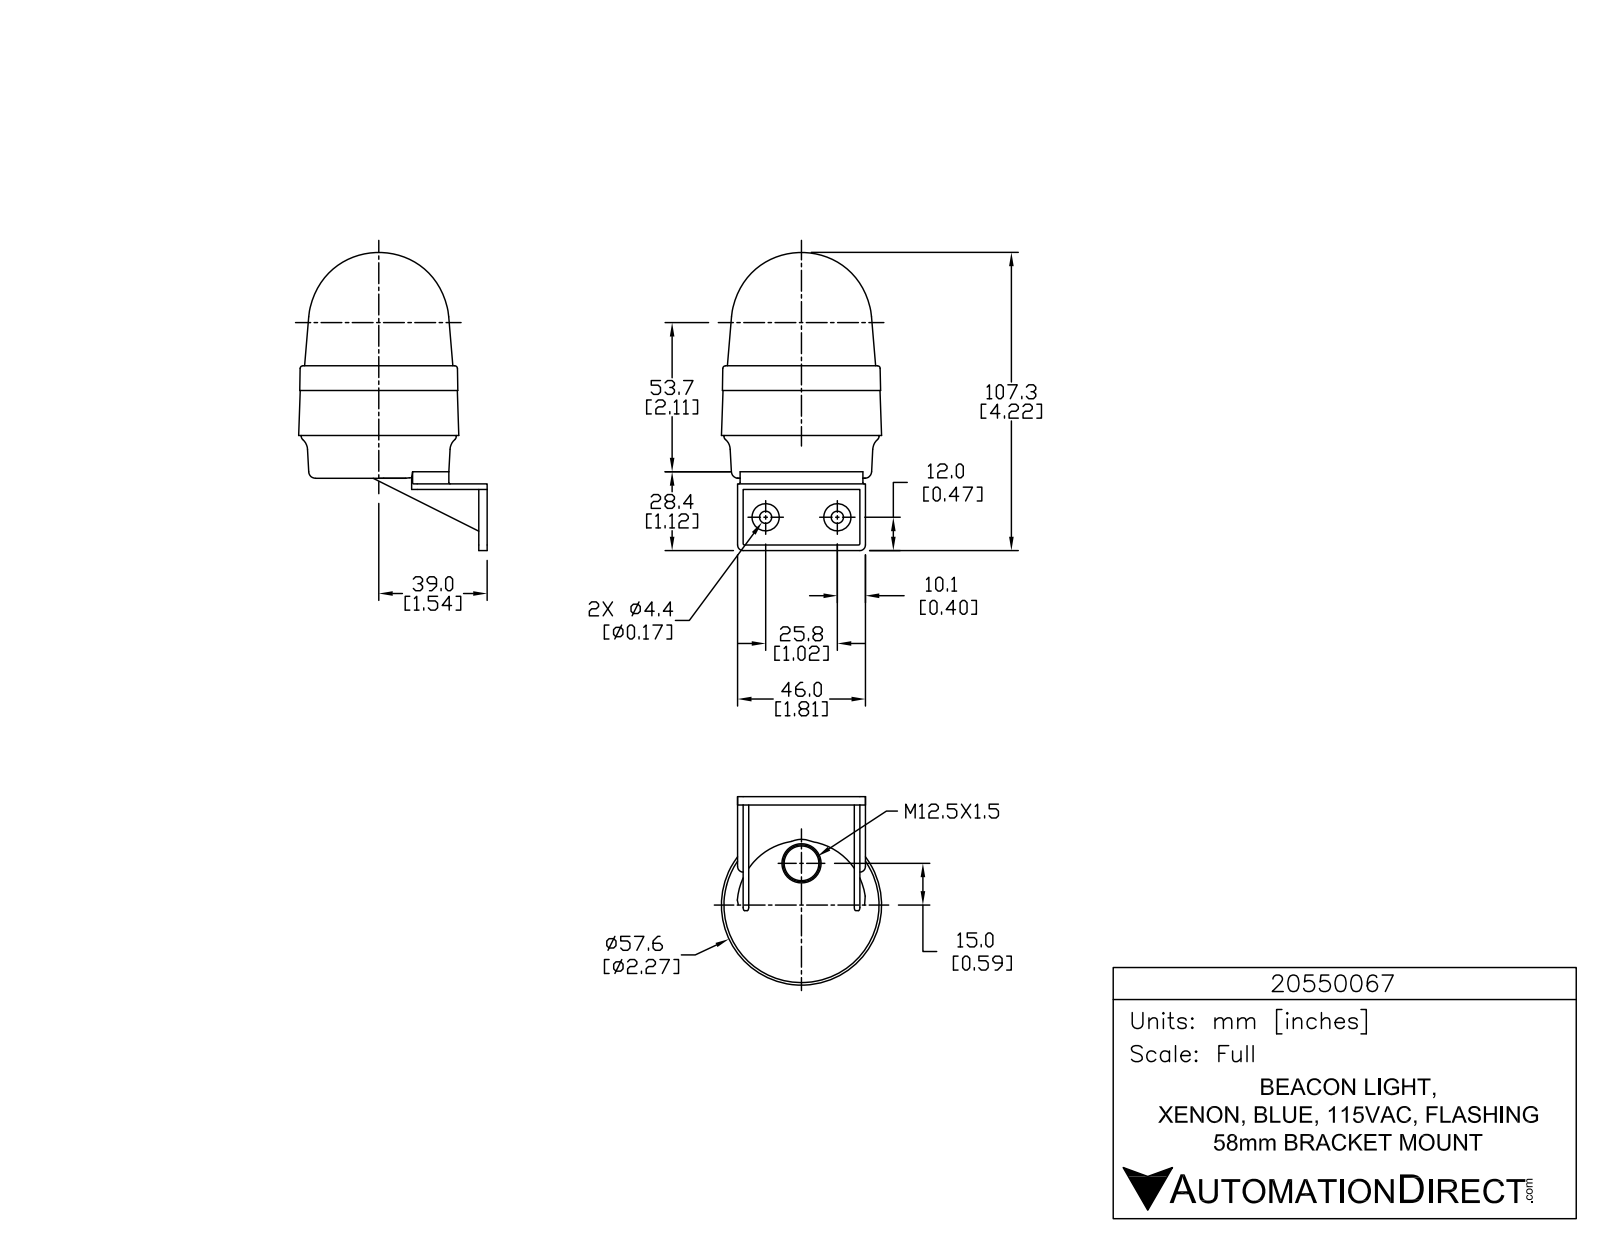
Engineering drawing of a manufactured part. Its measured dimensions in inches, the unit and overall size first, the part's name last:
Units: inches
Overall size (bounding box): 4.225 × 2.852 × 2.407
Round holes (diameter × count): ⌀0.039 ×3, ⌀0.173 ×2
Round bosses / shafts (diameter × count): ⌀0.226 ×3, ⌀0.056 ×3, ⌀0.386 ×2, ⌀2.197 ×1
Partial cylindrical surfaces — rounded edges, fillets, slot ends (radius × count): R0.008 ×6, R0.008 ×6, R0.008 ×6, R0.02 ×6, R0.131 ×6, R0.079 ×4, R0.004 ×3, R0.005 ×3
Main face-to-face distances: 0.079, 0.157, 1.575, 1.654, 0.039, 0.118, 1.496, 0.866, 0.945, 0.764
Hole centre spacings: 1.016
Volume: 10.27 in³ · Surface area: 33.38 in²
Bodies: 1 solid, 828 faces (551 planar, 179 cylindrical, 98 other)
Part name (STEP PRODUCT): 20550067
STEP written by: SolidWorks 2015 (AUTOMOTIVE_DESIGN)
